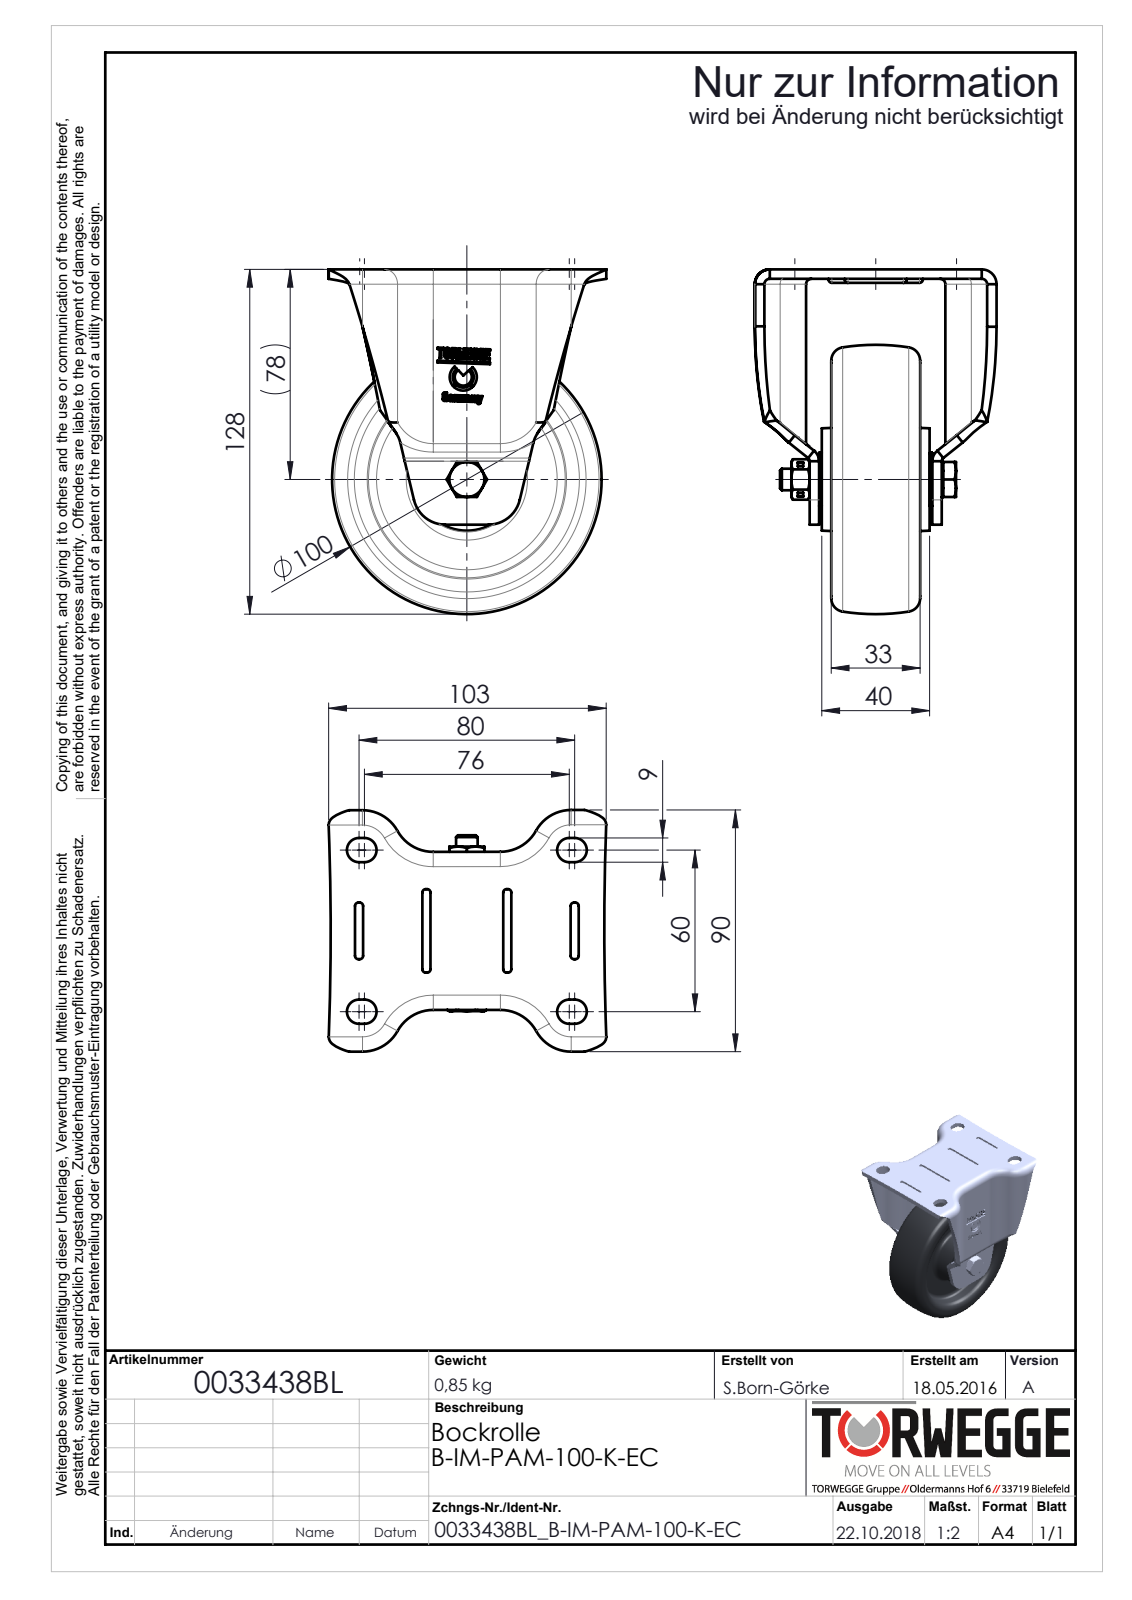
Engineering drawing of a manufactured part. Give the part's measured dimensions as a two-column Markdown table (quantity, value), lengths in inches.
| quantity | value |
| --- | --- |
| part name | 0033438BL_B-IM-PAM-100-K-EC |
| STEP written by | SolidWorks 2016 (AUTOMOTIVE_DESIGN) |
| units | inches |
| bodies | 13 solids, 756 faces (351 planar, 231 cylindrical, 174 other) |
| overall size | 5.039 × 4.056 × 3.533 |
| volume | 15.36 in³ |
| surface area | 141.1 in² |
| round holes (diameter × count) | 0.268 × 1, 0.315 × 1, 0.323 × 1, 0.472 × 1, 0.488 × 1, 0.661 × 1, 0.906 × 1, 0.913 × 1 |
| round bosses / shafts (diameter × count) | 1.102 × 1, 0.787 × 1, 0.591 × 1, 0.512 × 1, 0.469 × 1 |
| partial cylindrical surfaces (radius × count) | 0.049 × 20, 0.015 × 8, 0.138 × 8, 0.177 × 8, 0.008 × 7, 0.024 × 7, 0.079 × 5, 0.217 × 5 |
| main face-to-face distances | 0.138, 0.63, 1.024, 0.984, 1.982, 0.191, 0.394, 0.039, 1.614, 0.591 |
